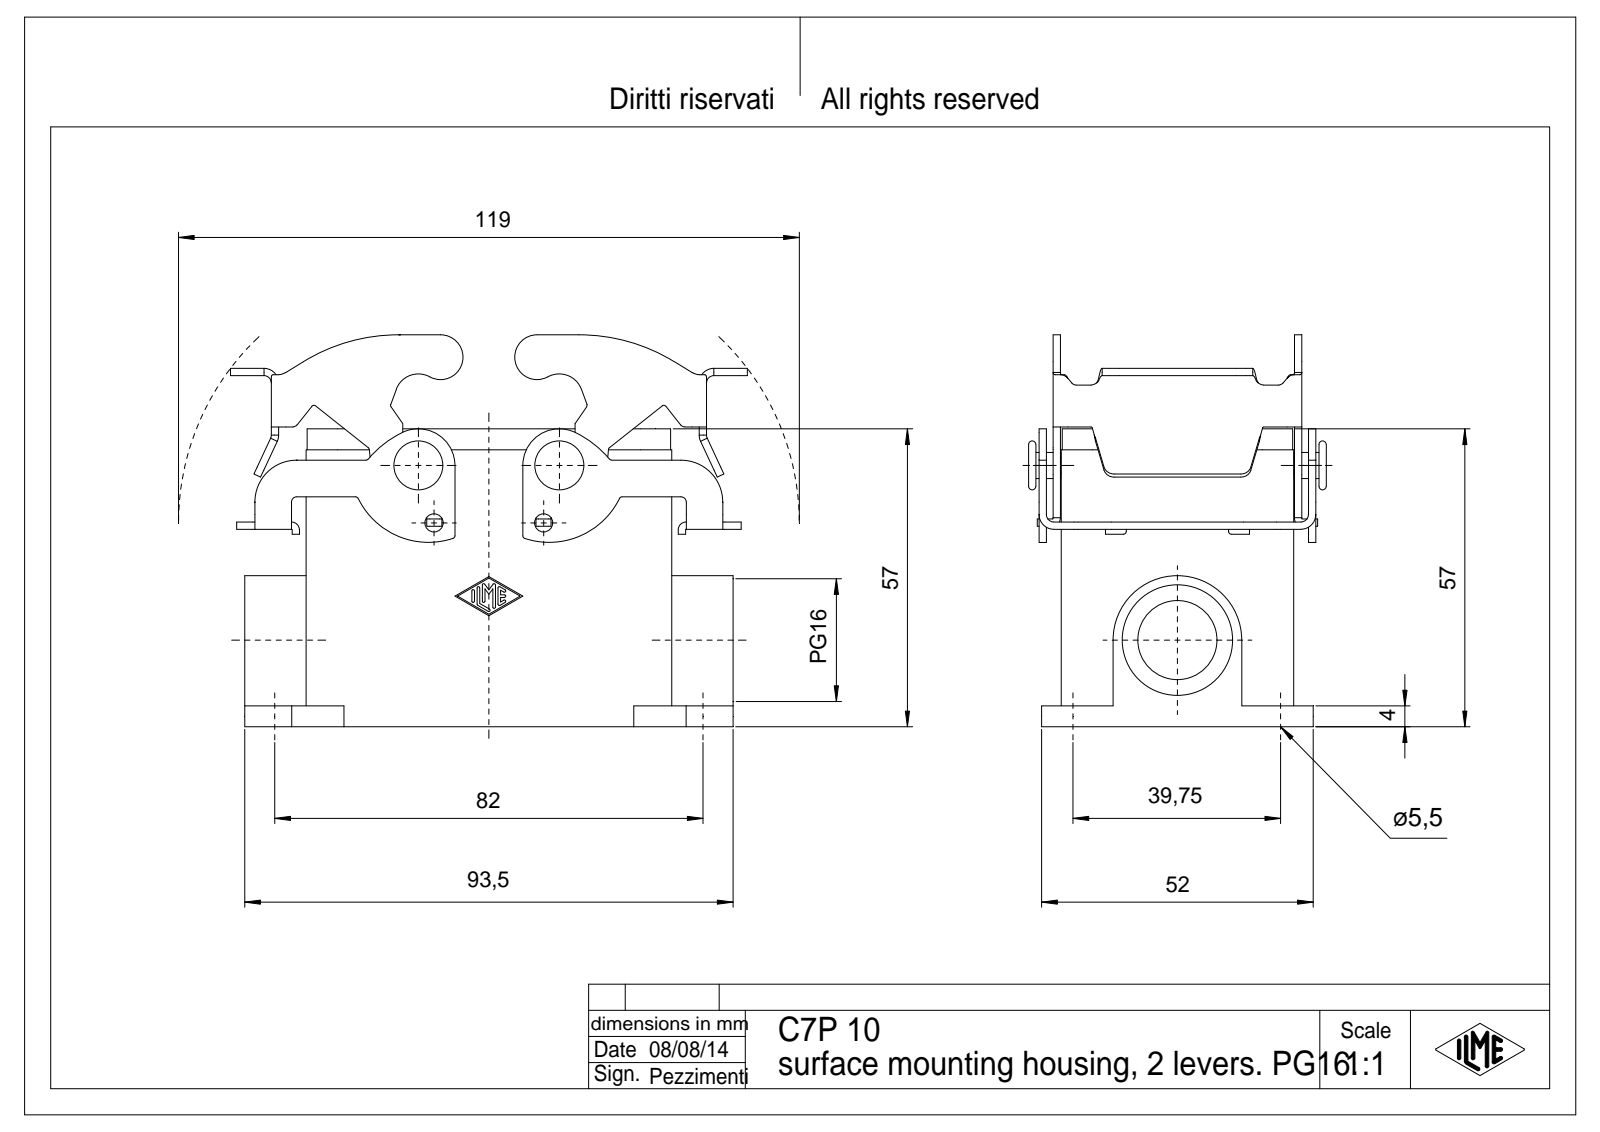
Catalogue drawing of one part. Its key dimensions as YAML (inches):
part_name: "p1; p2; p3; JCVP_10 (+1 more)"
step_written_by: "Creo Elements/Direct Modeling 18.0B 02-Dec-2011 (C) Parametric Technology GmbH (AUTOMOTIVE_DESIGN)"
units: inches
bodies: {solids: 3, faces: 609, planar: 293, cylindrical: 272, other: 44}
overall_size: [3.896, 2.953, 2.244]
volume: 5.243
surface_area: 80.06
round_holes:
  - {diameter: 0.097, count: 4}
  - {diameter: 0.118, count: 4}
  - {diameter: 0.217, count: 4}
  - {diameter: 0.138, count: 2}
  - {diameter: 0.597, count: 1}
  - {diameter: 0.833, count: 1}
round_bosses_or_shafts:
  - {diameter: 0.197, count: 2}
  - {diameter: 0.126, count: 2}
  - {diameter: 0.118, count: 2}
partial_cylinders:
  - {radius: 0.02, count: 22}
  - {radius: 0.039, count: 18}
  - {radius: 0.01, count: 16}
  - {radius: 0.059, count: 14}
  - {radius: 0.079, count: 12}
  - {radius: 0.055, count: 10}
  - {radius: 0.11, count: 10}
  - {radius: 0.315, count: 6}
face_to_face_distances: [0.157, 0.055, 1.594, 0.106, 1.925, 1.752, 1.437, 0.325, 0.061, 0.219]
hole_center_spacings: [0.555, 1.408, 2.748, 3.037, 1.063, 1.575, 2.244, 2.483]
